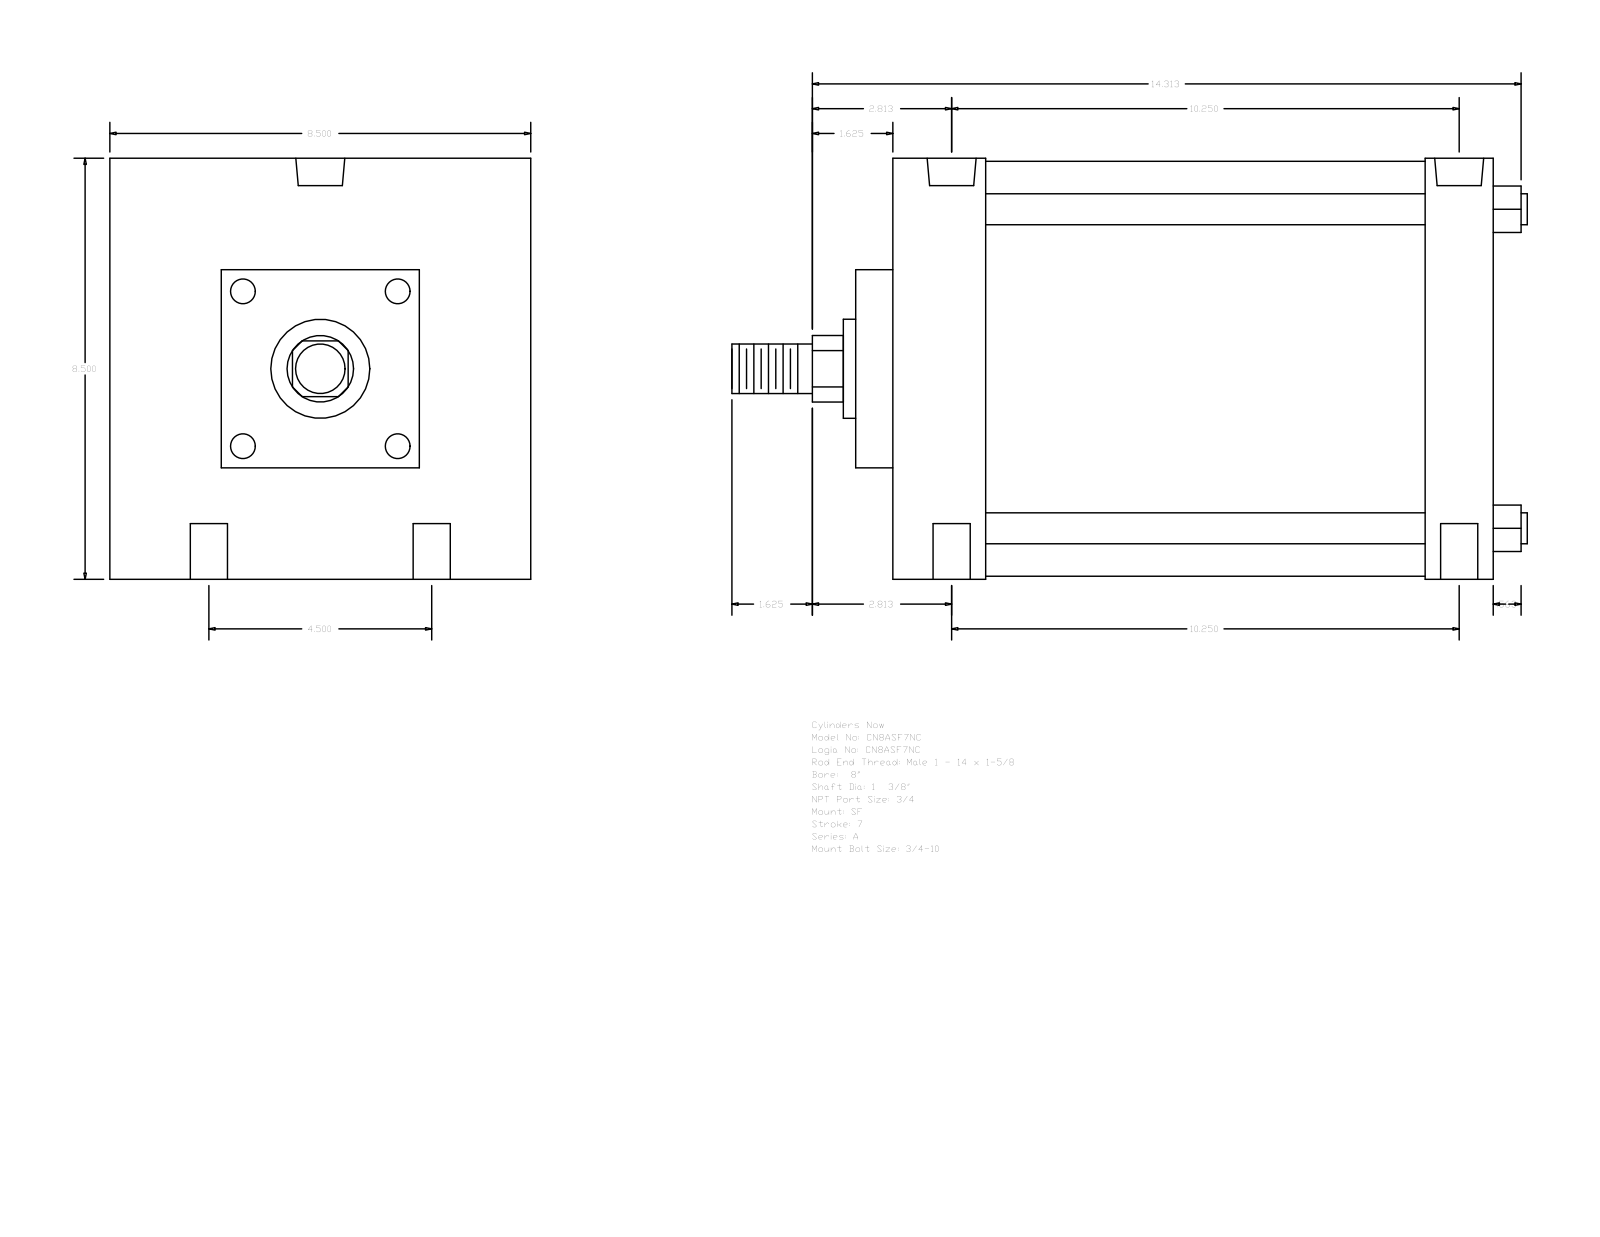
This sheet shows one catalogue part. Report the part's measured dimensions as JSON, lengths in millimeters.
{"part_name": "A_SF__0800_1.375", "step_written_by": "GSSL Pune (CONFIG_CONTROL_DESIGN)", "units": "millimeters", "bodies": {"solids": 0, "faces": 93, "planar": 67, "cylindrical": 26, "other": 0}, "overall_size": [407.99, 215.9, 215.9], "round_holes": [[19.05, 4], [15.08, 2], [25.12, 2]], "round_bosses_or_shafts": [[15.88, 4], [212.72, 1], [50.8, 1], [34.92, 1], [25.4, 1]], "partial_cylinders_radius": [[17.06, 1]], "face_to_face_distances": [307.98, 215.9, 47.63, 273.05, 225.42, 260.35, 34.93, 19.04, 66.67, 292.09], "hole_center_spacings": [57.15, 266.55, 260.35, 114.3, 284.34, 247.65]}
